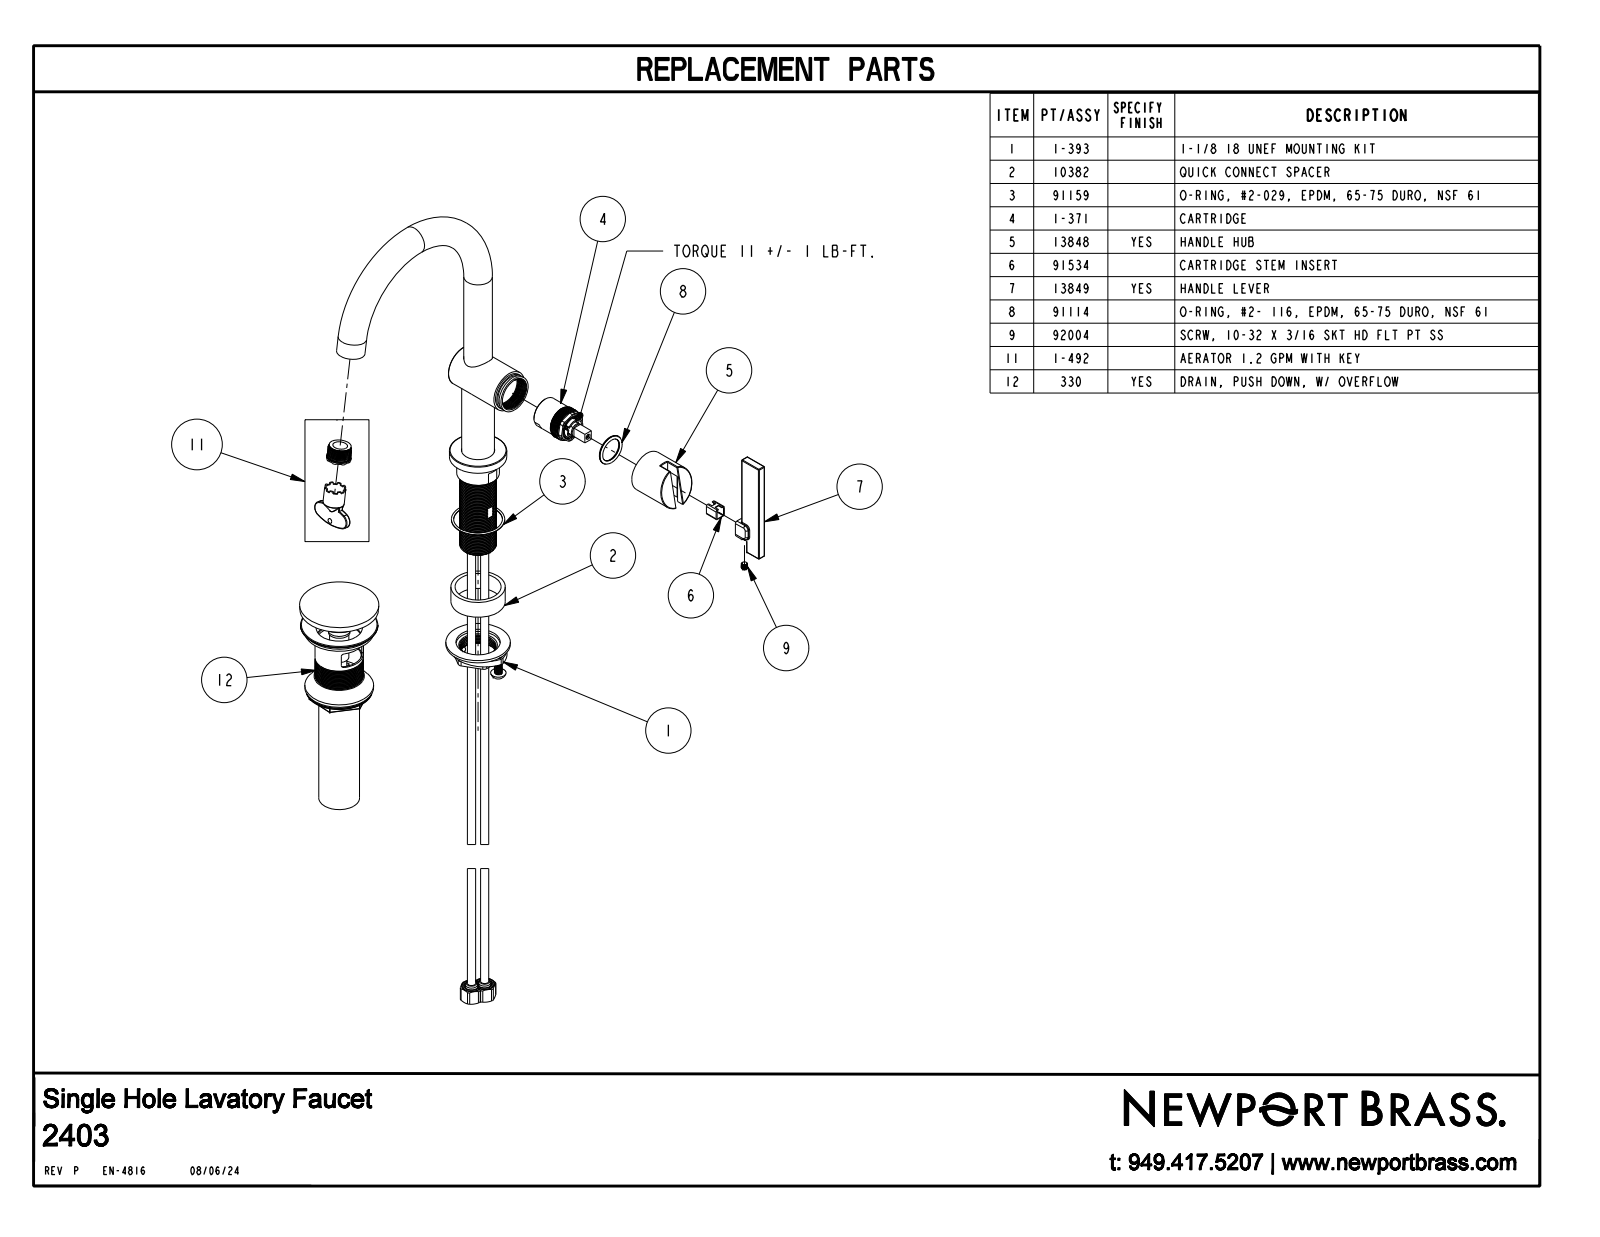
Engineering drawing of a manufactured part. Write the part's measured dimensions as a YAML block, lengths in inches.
part_name: "2403_SW0001"
step_written_by: "CREO PARAMETRIC BY PTC INC, 2018400 (AUTOMOTIVE_DESIGN)"
units: inches
bodies: {solids: 2, faces: 106, planar: 24, cylindrical: 38, other: 44}
overall_size: [9.432, 6.808, 3.84]
volume: 13
surface_area: 65.59
round_holes:
  - {diameter: 1.19, count: 1}
round_bosses_or_shafts:
  - {diameter: 0.875, count: 2}
  - {diameter: 1.75, count: 1}
  - {diameter: 1.25, count: 1}
partial_cylinders:
  - {radius: 0.02, count: 20}
  - {radius: 0.03, count: 4}
face_to_face_distances: [0.25, 0.25, 3.59, 2.61, 0.98, 2.79, 0.18, 0.8, 2.836, 0.226]
